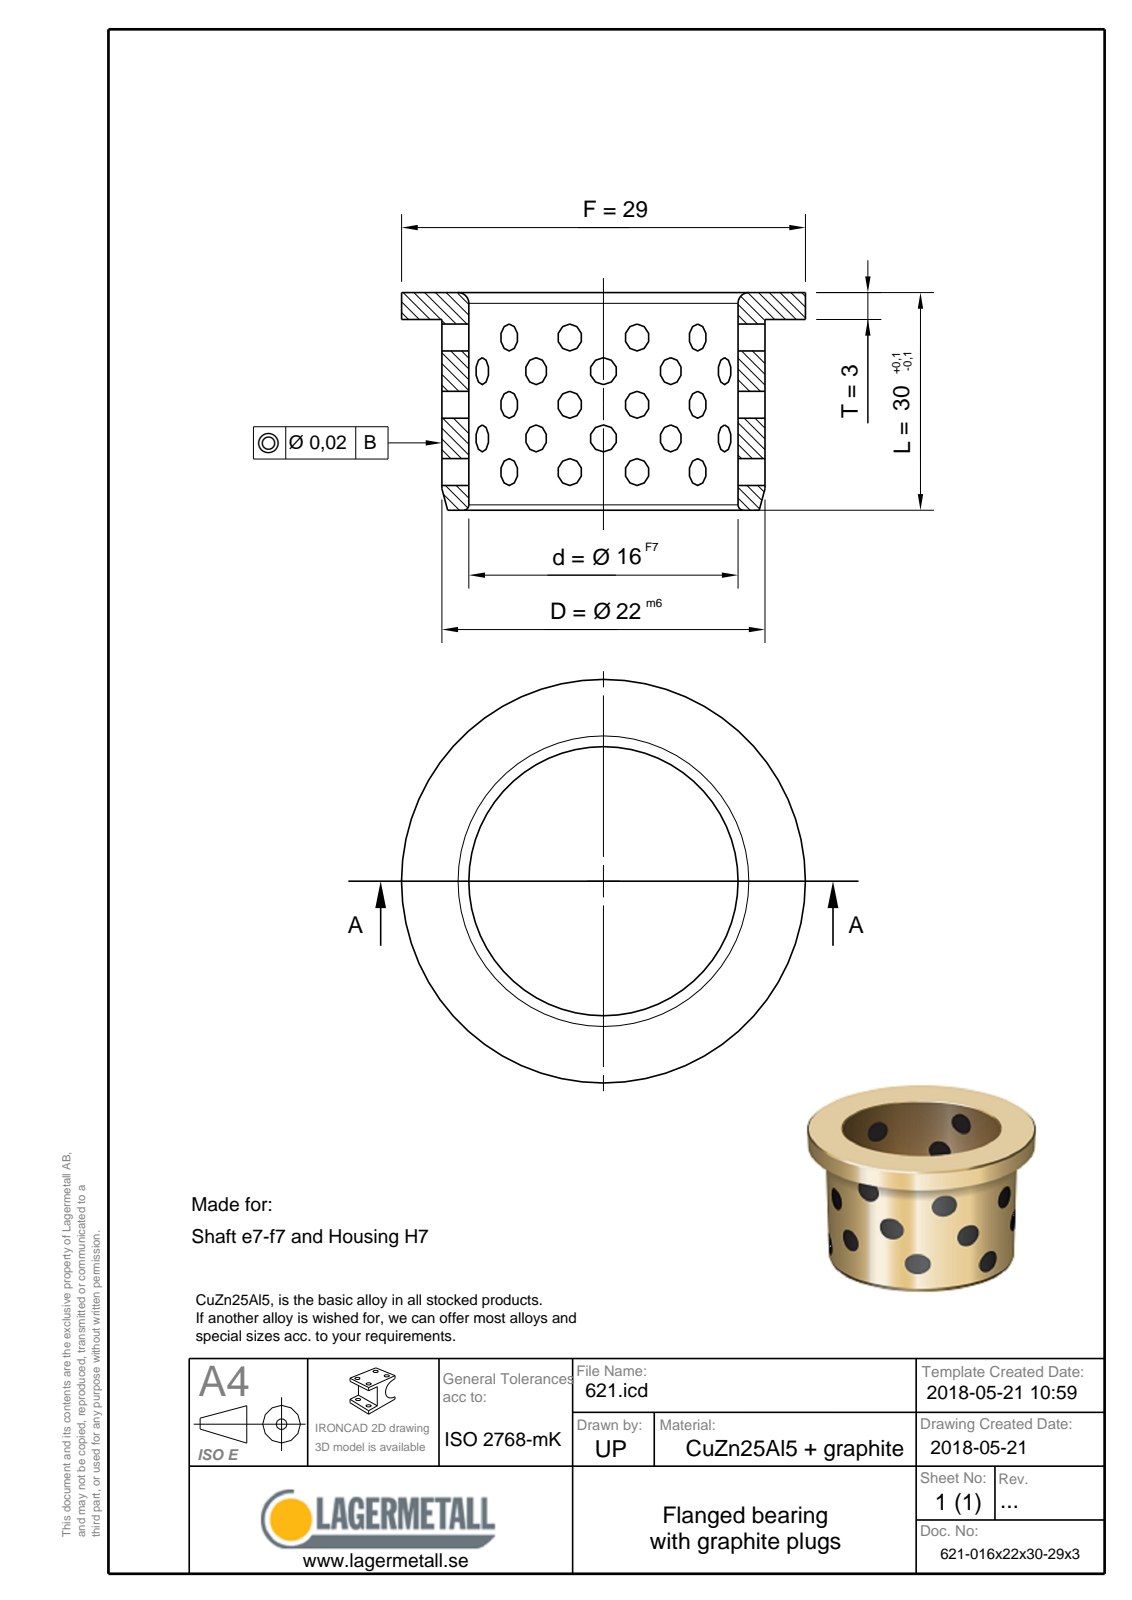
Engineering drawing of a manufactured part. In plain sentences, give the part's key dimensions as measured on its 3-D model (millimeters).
The part is named "621-016x22x30-29x3". Its 3-D file was written by "Spatial InterOp 3D (CONFIG_CONTROL_DESIGN)". It is 1 solid with 9 faces: 3 planar, 3 cylindrical and 3 other. Overall it measures 30 by 29 by 29 millimeters. Its volume is 6 115 cubic millimeters and its surface area 4 459 square millimeters. Round holes: 1 of diameter 16. Round bosses or shafts: 1 of diameter 29, 1 of diameter 22. The main face-to-face distances are 3, 27, 30.
